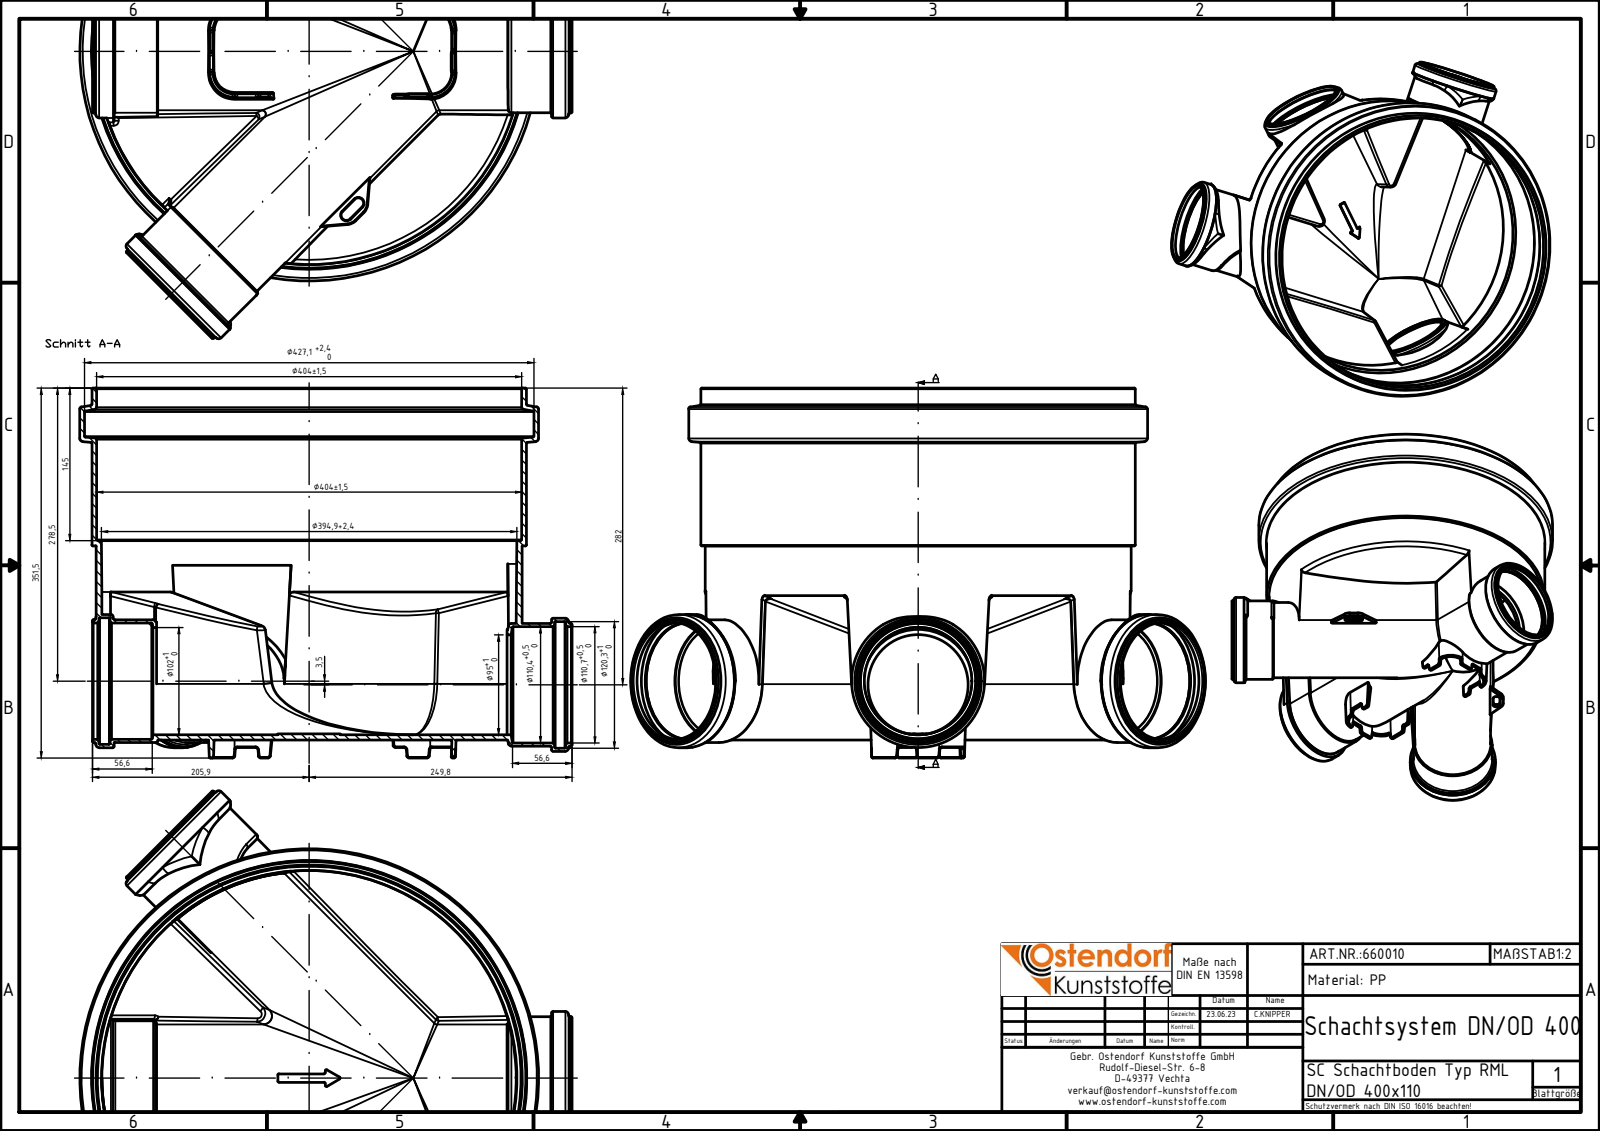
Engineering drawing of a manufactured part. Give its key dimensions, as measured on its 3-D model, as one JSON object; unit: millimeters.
{"part_name": "660010", "step_written_by": "Autodesk Inventor 2020 (AUTOMOTIVE_DESIGN)", "units": "millimeters", "bodies": {"solids": 1, "faces": 644, "planar": 121, "cylindrical": 191, "other": 332}, "overall_size": [546.29, 467.85, 351.5], "volume_mm3": 2986000, "surface_area_mm2": 1295000, "round_holes": [[110.7, 6], [110.4, 4], [120.3, 4], [102, 3], [95, 1], [404, 1], [427.1, 1]], "round_bosses_or_shafts": [[126.5, 4], [116.9, 4], [116.6, 4], [436.1, 1], [413, 1], [404.9, 1]], "partial_cylinders_radius": [[1, 82], [2, 32], [56, 5], [5, 4], [11.5, 4], [3.5, 3], [4, 2], [8, 2]], "face_to_face_distances": [5, 7.3, 150, 145, 2.29, 7.29, 2.3, 112, 4.97, 137], "hole_center_spacings": [3.5]}
